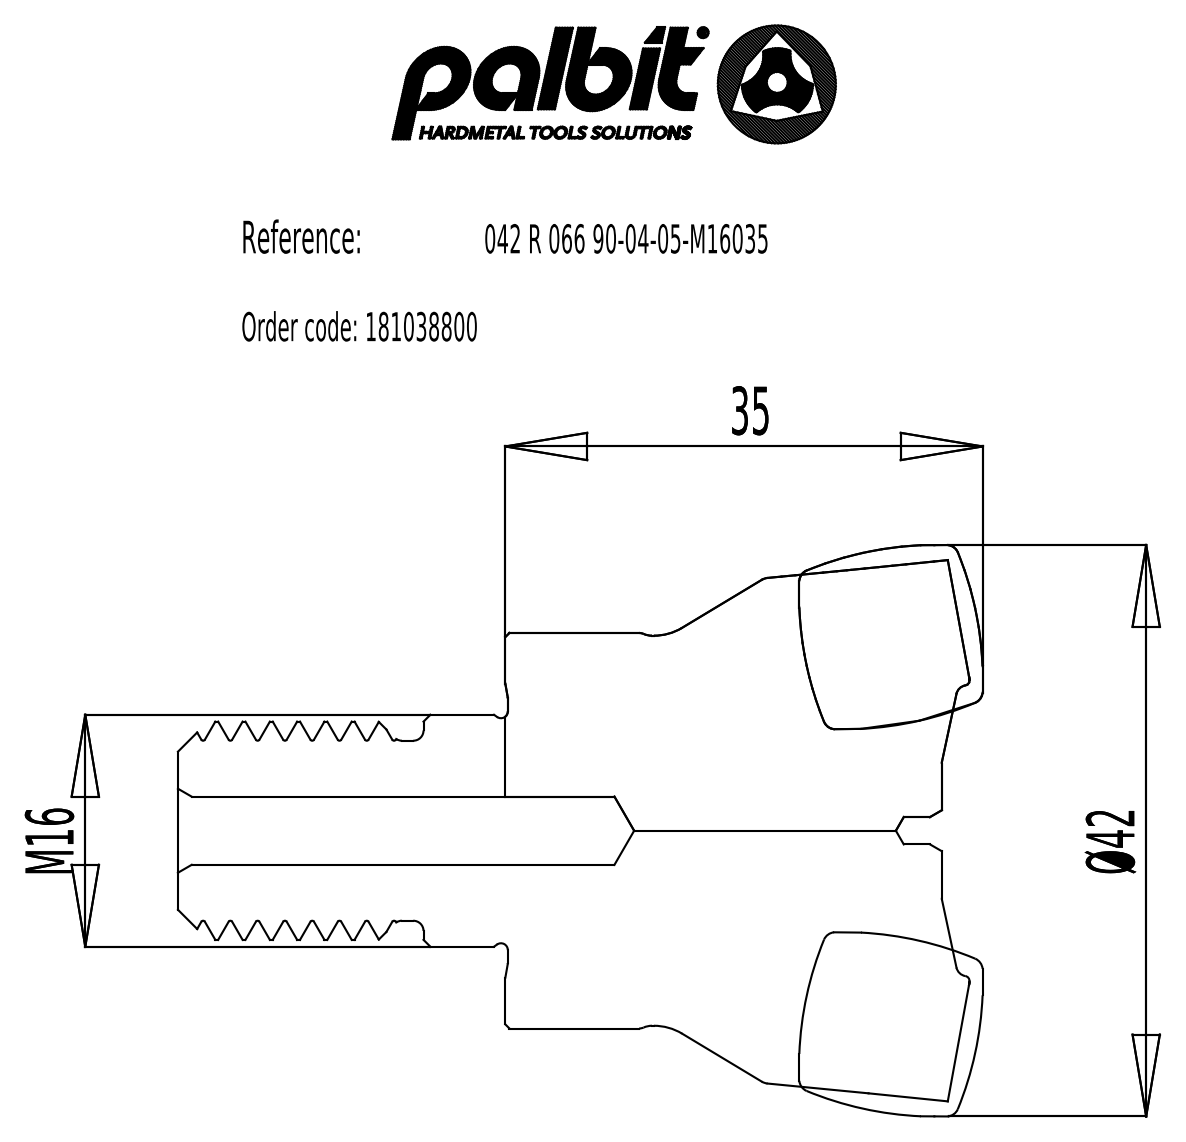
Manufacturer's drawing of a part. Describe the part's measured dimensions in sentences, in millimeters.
The part is named "NOCUT^CUT PROFILE - 181038800; CUT^CUT PROFILE - 181038800; CUT PROFILE - 181038800". Its 3-D file was written by "SolidWorks 2015 (CONFIG_CONTROL_DESIGN)". It is 2 solids with 89 faces: 7 planar, 12 cylindrical and 70 other. Overall it measures 58.99 by 41.9 by 41.9 millimeters. Its volume is 47 422 cubic millimeters and its surface area 11 758 square millimeters. Round holes: 1 of diameter 2, 1 of diameter 5. Round bosses or shafts: 1 of diameter 29, 1 of diameter 28.6, 1 of diameter 17, 1 of diameter 16, 1 of diameter 13.2. The main face-to-face distances are 21.55, 13.44, 34.99, 58.99, 45.55, 24, 2.99, 10.45, 32, 56.
